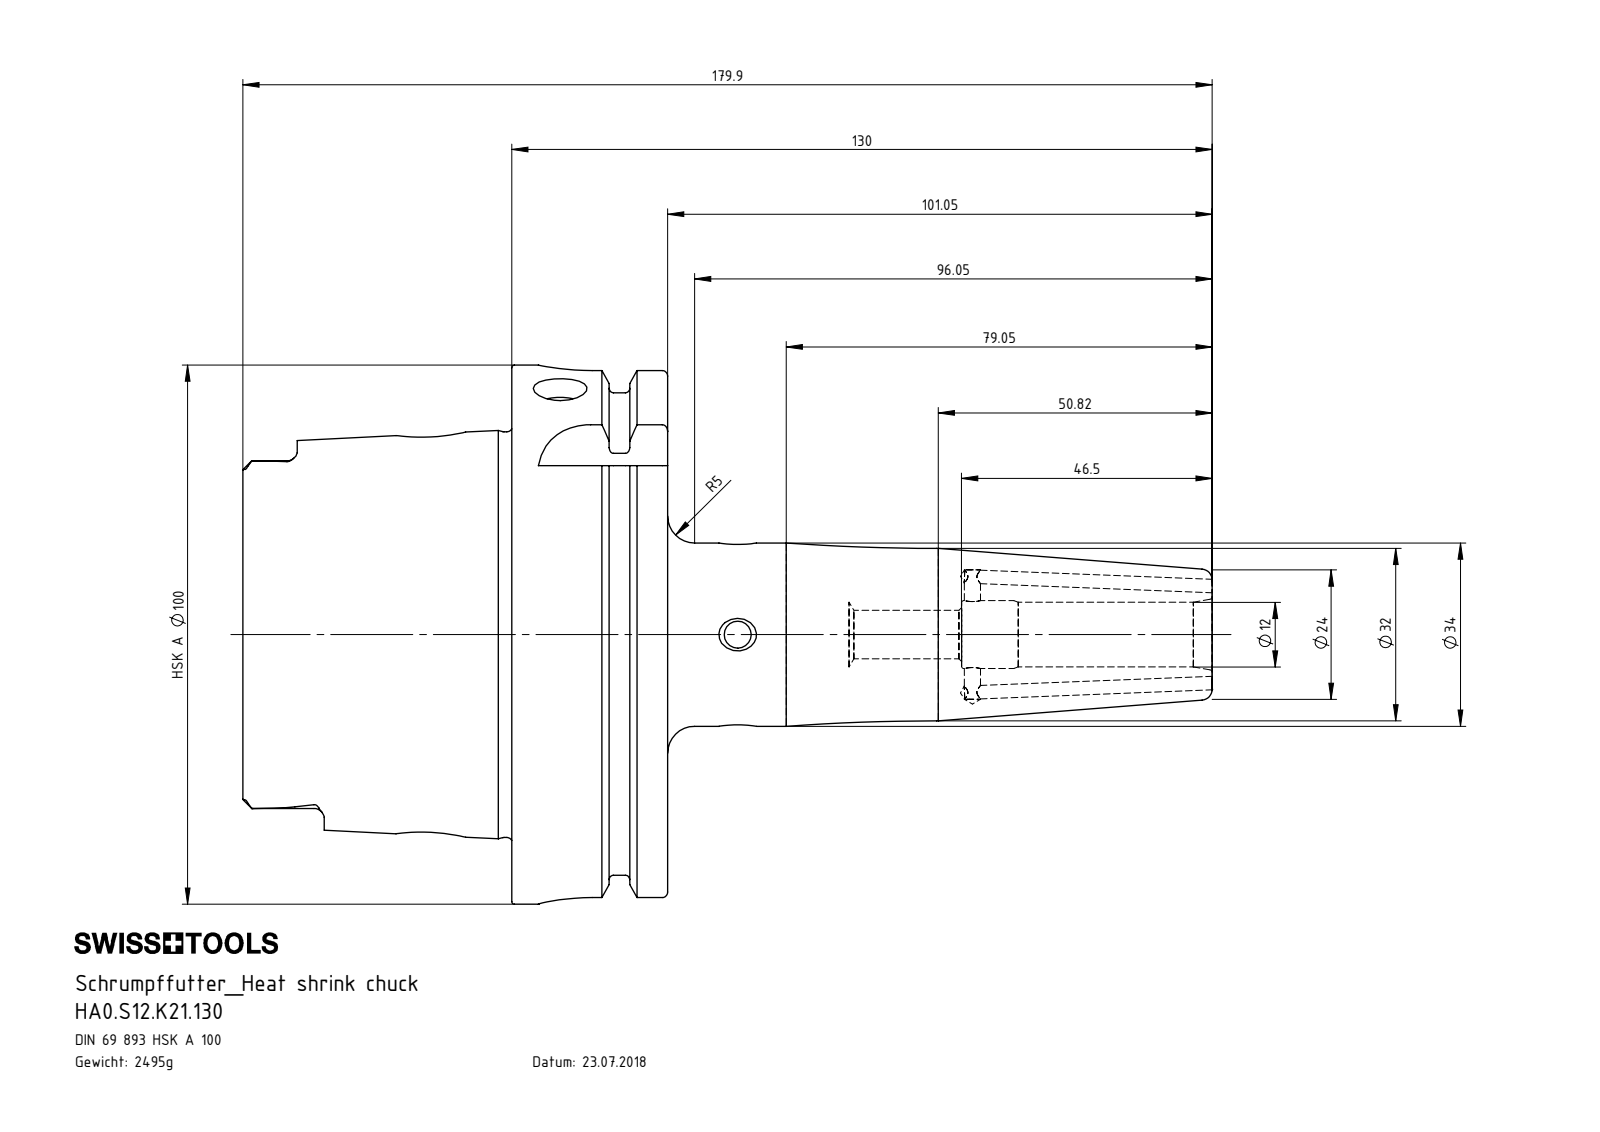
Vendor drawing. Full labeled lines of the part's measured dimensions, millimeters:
Part name (STEP PRODUCT): HA0-S12.K21.130_C_Fertigbearbeitung; ERU-AN4.K01.020_A; ERU-CJ2.001.006; HA0.S12.K21.130
STEP written by: SolidWorks 2017 (CONFIG_CONTROL_DESIGN)
Units: millimetres
Bodies: 4 solids, 301 faces (95 planar, 89 cylindrical, 117 other)
Overall size (bounding box): 179.98 × 100 × 100
Volume: 317 877 mm³ · Surface area: 64 833 mm²
Round holes (diameter × count): ⌀5 ×3, ⌀10 ×3, ⌀2.5 ×2, ⌀12 ×2, ⌀3 ×1, ⌀9 ×1, ⌀12.6 ×1, ⌀22.5 ×1, ⌀26 ×1, ⌀53 ×1, ⌀63 ×1
Round bosses / shafts (diameter × count): ⌀3 ×2, ⌀100 ×1, ⌀91.95 ×1, ⌀75.26 ×1, ⌀34 ×1, ⌀32 ×1, ⌀10 ×1
Partial cylindrical surfaces — rounded edges, fillets, slot ends (radius × count): R1.9 ×6, R4.88 ×4, R10 ×4
Main face-to-face distances: 28.95, 16.5, 12.45, 49.9, 62.35, 78.85, 87.8, 78.2, 28.3, 15.85
Hole centre spacings: 34.95, 43.55, 56.95, 100.5
